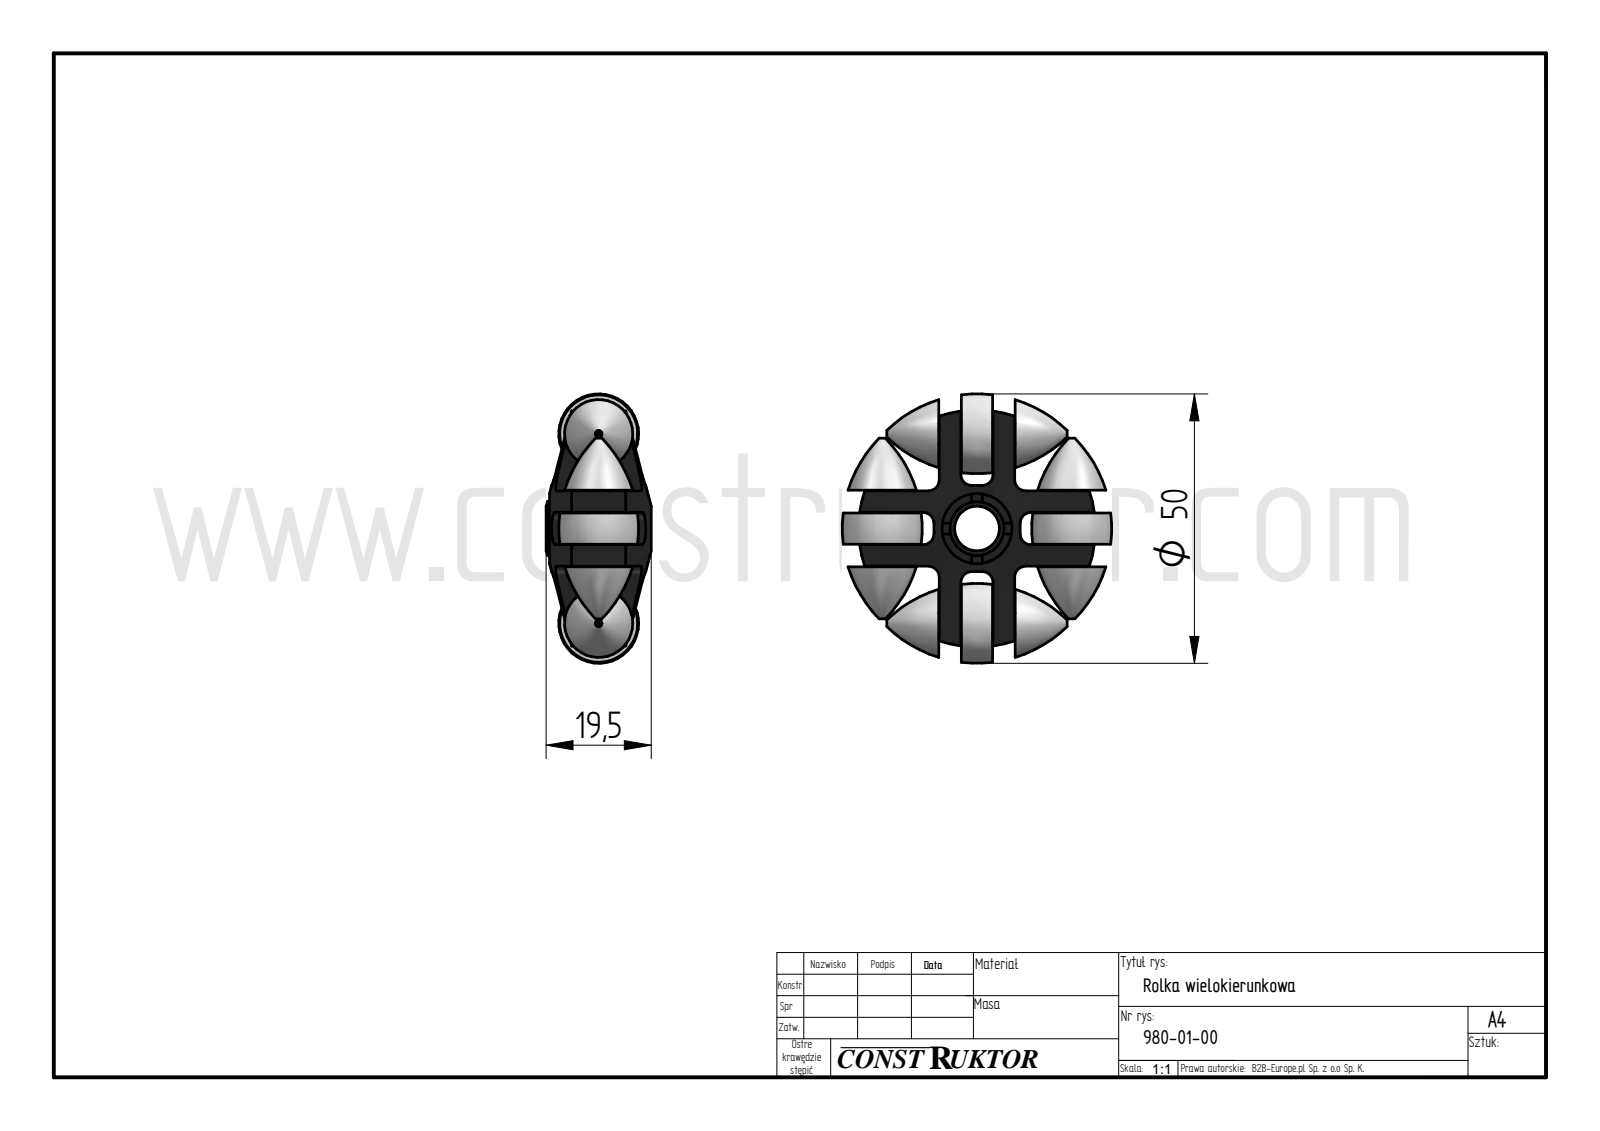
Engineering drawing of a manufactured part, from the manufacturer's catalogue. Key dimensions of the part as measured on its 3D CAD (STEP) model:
Part name (STEP PRODUCT): 980-01-00; 980-01-01; 980-01-02
STEP written by: ST-DEVELOPER v16.7 (AUTOMOTIVE_DESIGN)
Units: millimetres
Bodies: 5 solids, 118 faces (60 planar, 43 cylindrical, 15 other)
Overall size (bounding box): 50 × 50 × 19.5
Volume: 17 630 mm³ · Surface area: 11 876 mm²
Round holes (diameter × count): ⌀0.2 ×4, ⌀4 ×4, ⌀8.3 ×1, ⌀13 ×1
Round bosses / shafts (diameter × count): ⌀3.8 ×4, ⌀10 ×1
Partial cylindrical surfaces — rounded edges, fillets, slot ends (radius × count): R2 ×12, R22 ×1
Main face-to-face distances: 4.1, 10, 4, 5.9, 9.9, 4.2, 10.1, 14.1, 5.8, 6
Hole centre spacings: 35.18
